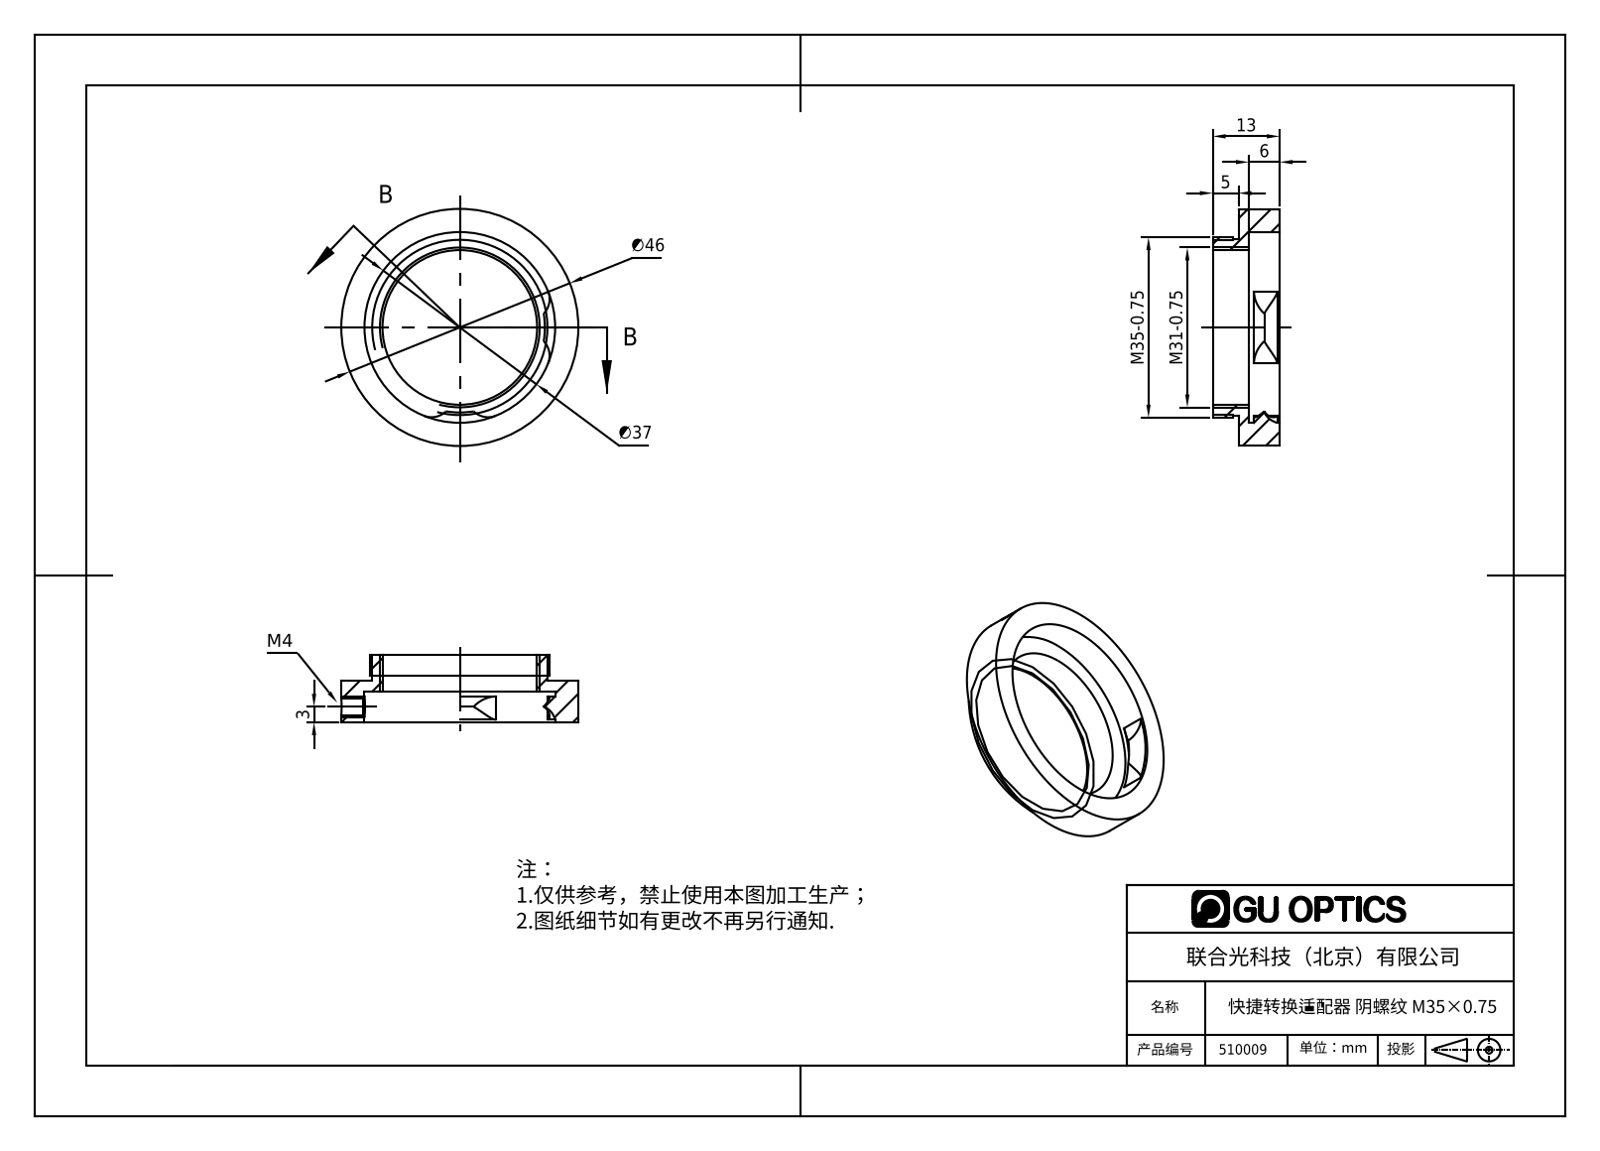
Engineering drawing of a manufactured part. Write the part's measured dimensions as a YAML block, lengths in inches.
part_name: "510009"
step_written_by: "SolidWorks 2016 (CONFIG_CONTROL_DESIGN)"
units: inches
bodies: {solids: 1, faces: 30, planar: 5, cylindrical: 19, other: 6}
overall_size: [1.811, 1.811, 0.512]
volume: 0.409
surface_area: 7.922
round_holes:
  - {diameter: 0.13, count: 1}
  - {diameter: 0.159, count: 1}
  - {diameter: 1.181, count: 1}
  - {diameter: 1.457, count: 1}
round_bosses_or_shafts:
  - {diameter: 1.811, count: 1}
  - {diameter: 1.378, count: 1}
  - {diameter: 1.346, count: 1}
partial_cylinders:
  - {radius: 0.157, count: 4}
face_to_face_distances: [0.315, 0.079, 0.236, 0.197, 0.276, 0.512, 0.157, 0.039, 0.118, 0.354]
